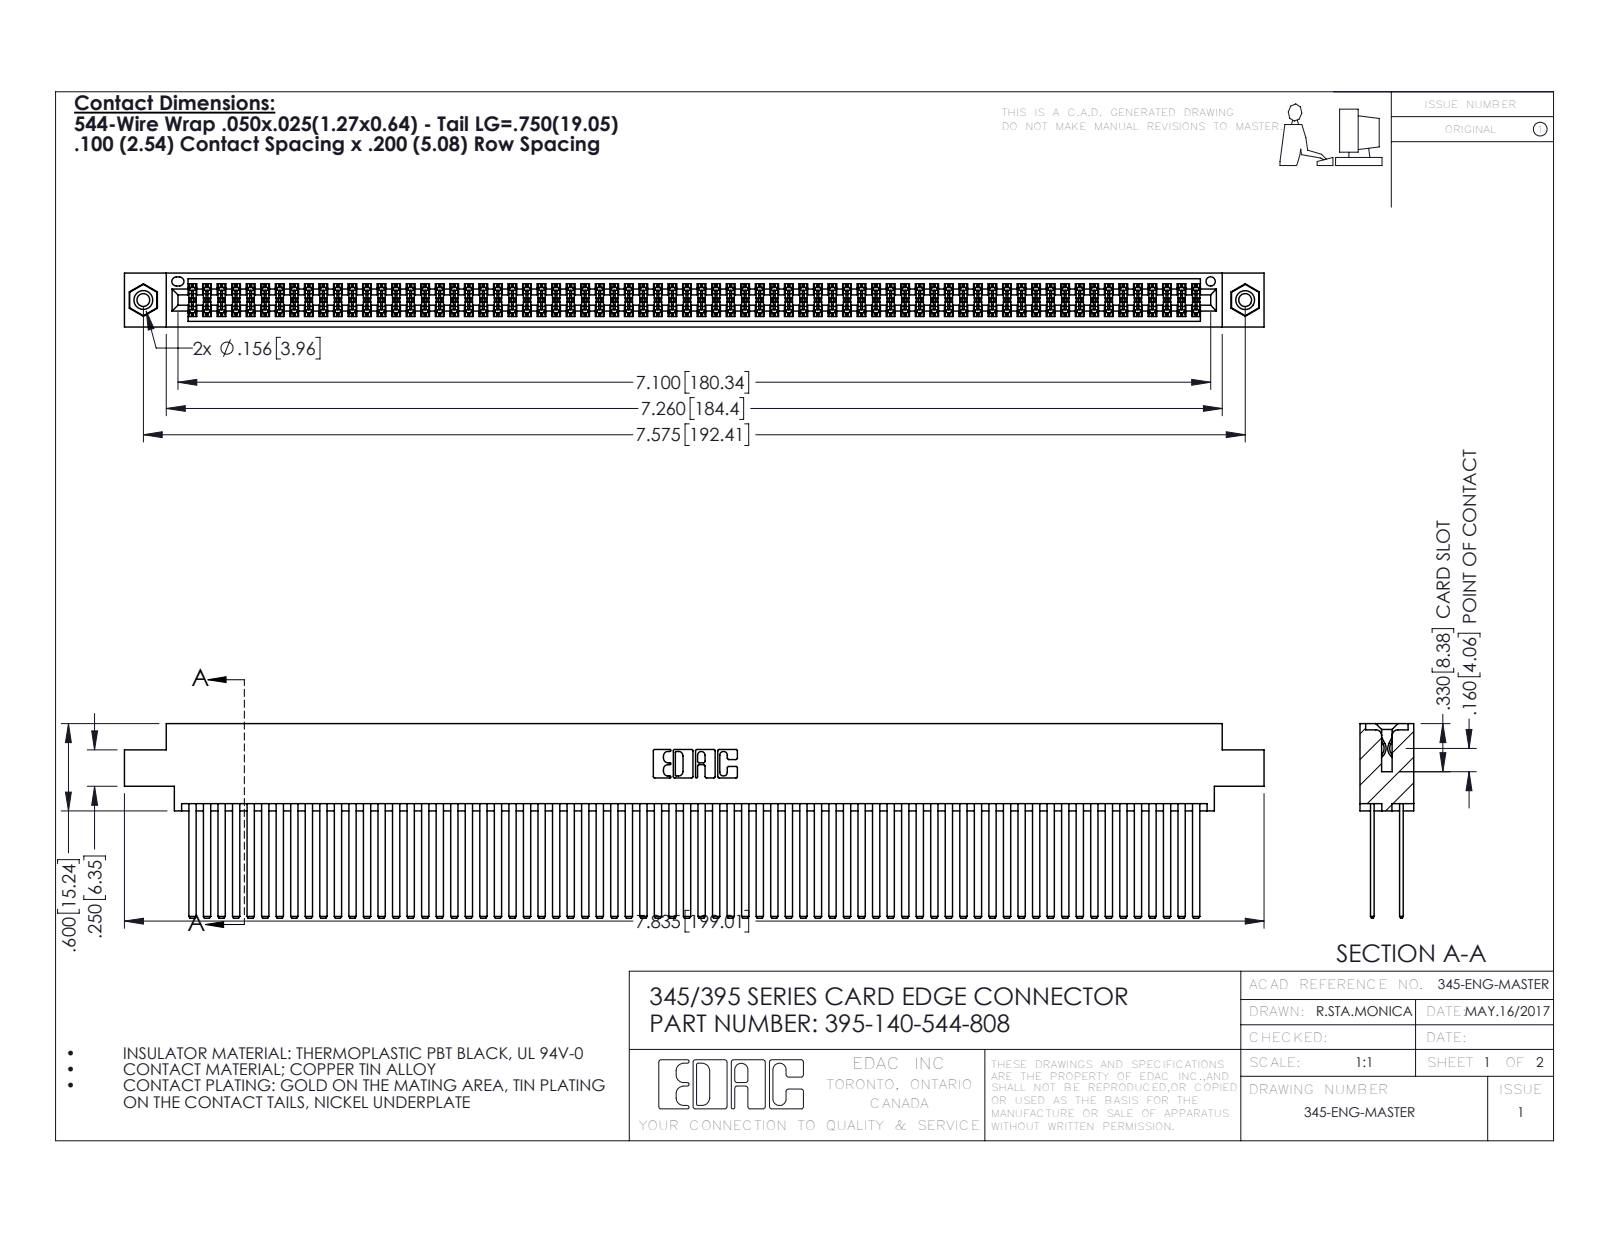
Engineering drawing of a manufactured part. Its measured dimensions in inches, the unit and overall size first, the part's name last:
Units: inches
Overall size (bounding box): 7.835 × 1.337 × 0.37
Round holes (diameter × count): ⌀0.089 ×2, ⌀0.125 ×2, ⌀0.156 ×2, ⌀0.064 ×1
Round bosses / shafts (diameter × count): ⌀0.155 ×2
Partial cylindrical surfaces — rounded edges, fillets, slot ends (radius × count): R0.006 ×210, R0.01 ×22, R0.007 ×6, R0.031 ×6, R0.026 ×3, R0.014 ×2, R0.019 ×2, R0.022 ×2
Main face-to-face distances: 0.2, 0.025, 0.072, 0.098, 0.272, 0.298, 0.225, 0.175, 0.37, 0.149
Hole centre spacings: 0.27, 7.339, 7.575
Volume: 1.308 in³ · Surface area: 59.11 in²
Bodies: 143 solids, 6350 faces (4176 planar, 2158 cylindrical, 16 other)
Part name (STEP PRODUCT): 345 Part_0.170 Offset - 0.156 Dia-TI; 395-140-544-808; 345-292-001_345-293-144; 345-250-001_345-250-003-102
STEP written by: SolidWorks 2016 (CONFIG_CONTROL_DESIGN)
